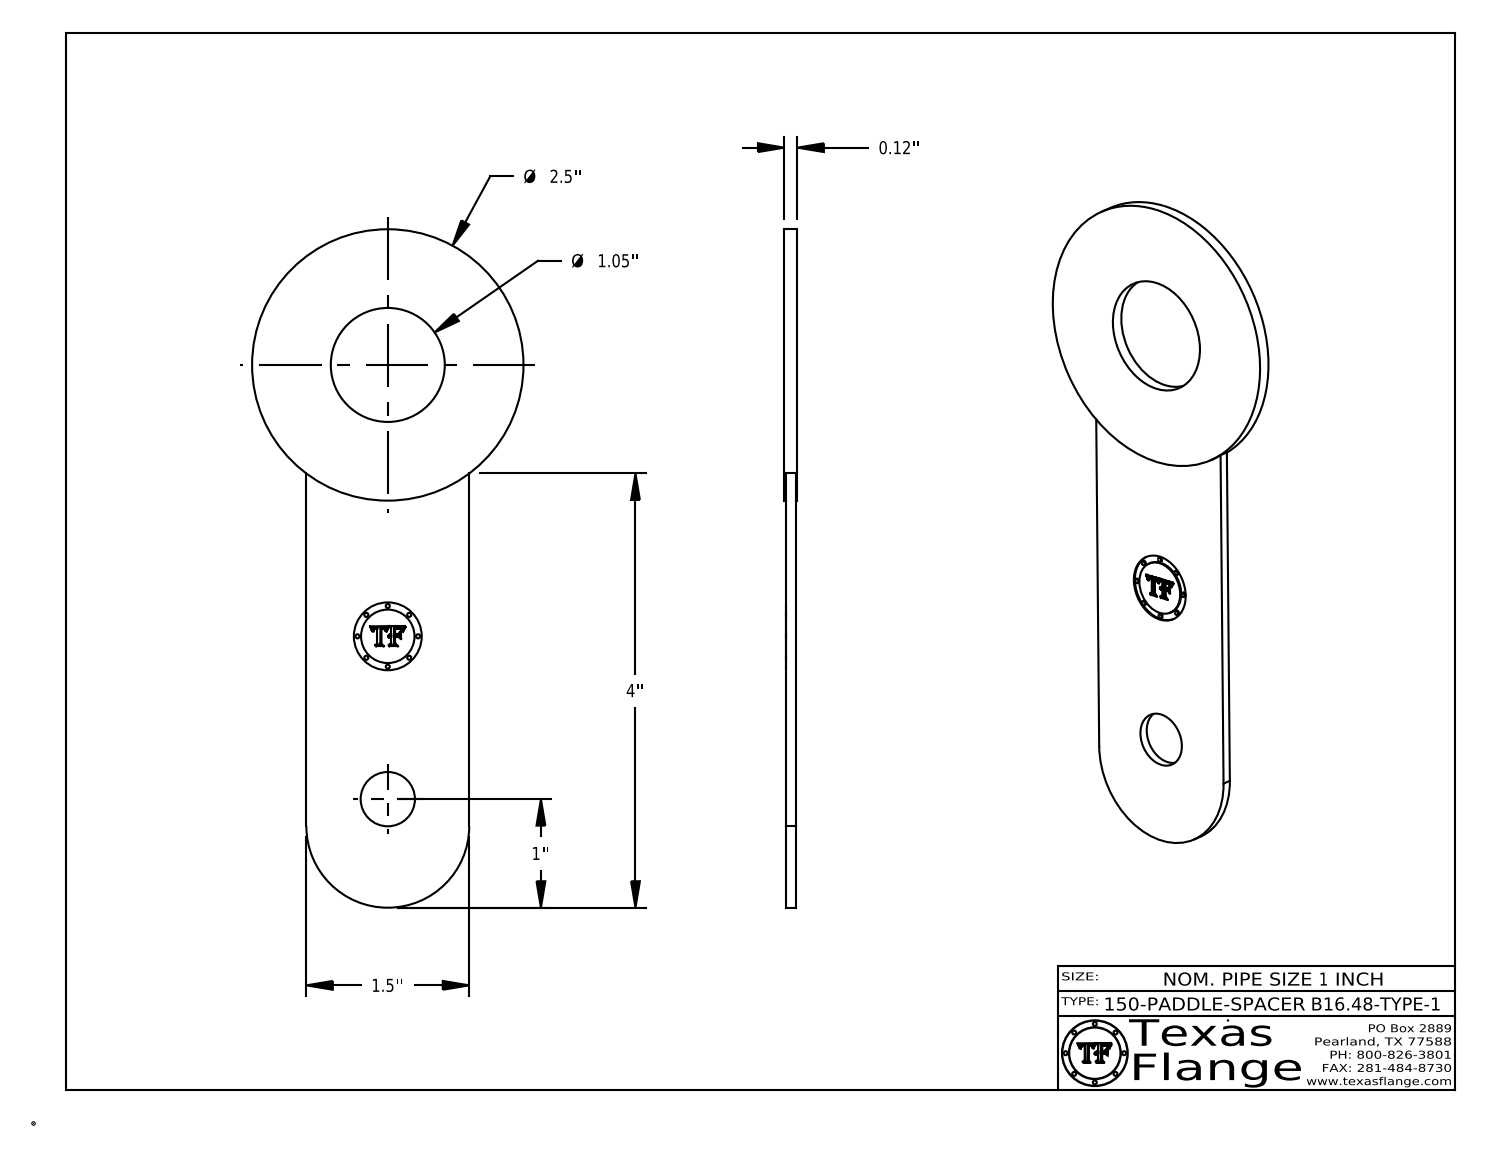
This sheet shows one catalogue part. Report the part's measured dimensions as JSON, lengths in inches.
{"part_name": "1-150-PADDLE-SPACER-B16.48-TYPE-2", "step_written_by": "CATIA V5 STEP AP214 (AUTOMOTIVE_DESIGN)", "units": "inches", "bodies": {"solids": 1, "faces": 398, "planar": 371, "cylindrical": 27, "other": 0}, "overall_size": [6.25, 2.5, 0.12], "volume_in3": 0.961, "surface_area_in2": 20.95, "round_holes": [[0.5, 1], [0.625, 1], [1.05, 1]], "round_bosses_or_shafts": [[0.038, 8], [2.5, 1], [0.492, 1]], "partial_cylinders_radius": [[0.75, 1]], "face_to_face_distances": [0.015, 0.105, 0.09, 0.12, 1.5, 0.075, 0.03, 0.687, 0.813, 0.186], "hole_center_spacings": [1.5, 2.5, 4]}
